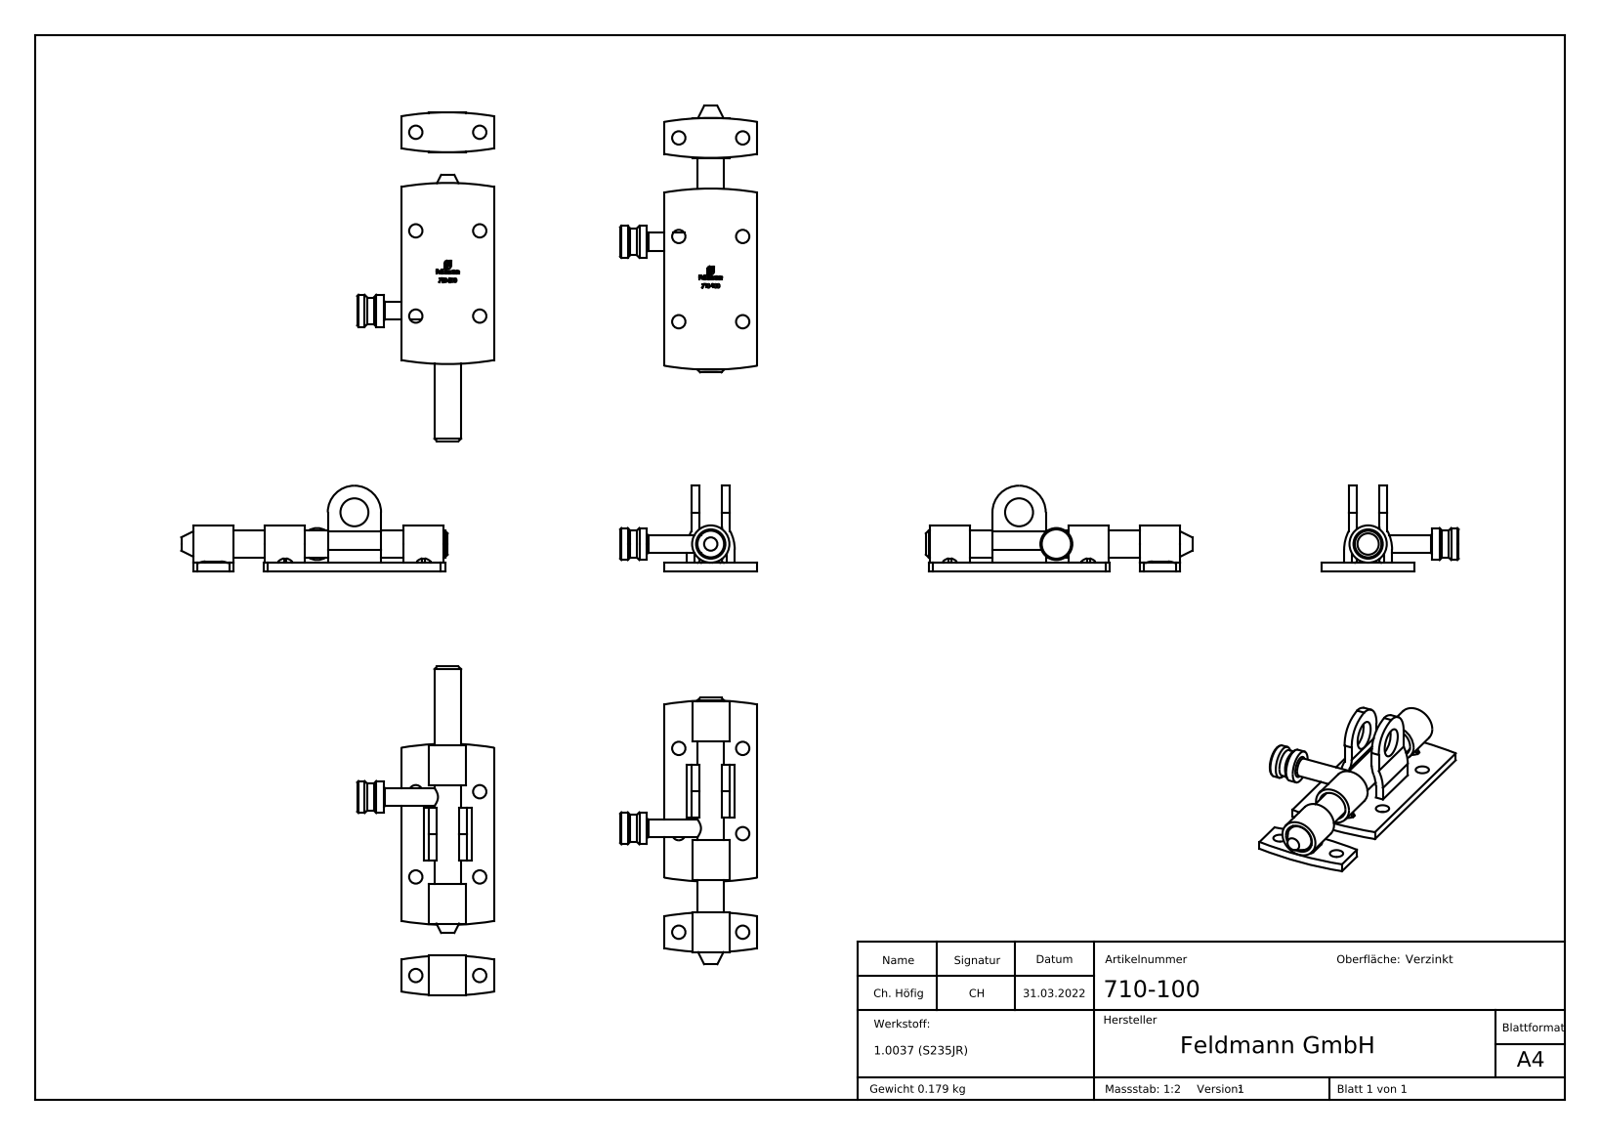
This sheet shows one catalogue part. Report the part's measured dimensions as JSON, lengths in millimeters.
{"part_name": "710-XX0 Teil1_710-100 Teil1; 710-100; 710-XX0 Teil2_710-100 Teil2; 710-XX0 Teil3_710-100 Teil3", "step_written_by": "SolidWorks 2018 (CONFIG_CONTROL_DESIGN)", "units": "millimeters", "bodies": {"solids": 3, "faces": 308, "planar": 154, "cylindrical": 39, "other": 115}, "overall_size": [100, 51.5, 32], "volume_mm3": 22969, "surface_area_mm2": 16733, "round_holes": [[5, 6], [10.5, 1], [11, 1]], "round_bosses_or_shafts": [[10, 2], [14, 1], [12, 1], [6.8, 1]], "partial_cylinders_radius": [[102.83, 4], [10, 3], [1, 2], [2, 2], [11.88, 2], [14.88, 2]], "face_to_face_distances": [3, 13.25, 10.25, 11.5, 8.5, 15, 24.75, 1.75, 21.75, 23.5], "hole_center_spacings": [24, 32, 37, 40, 44.1, 69, 73.05]}
